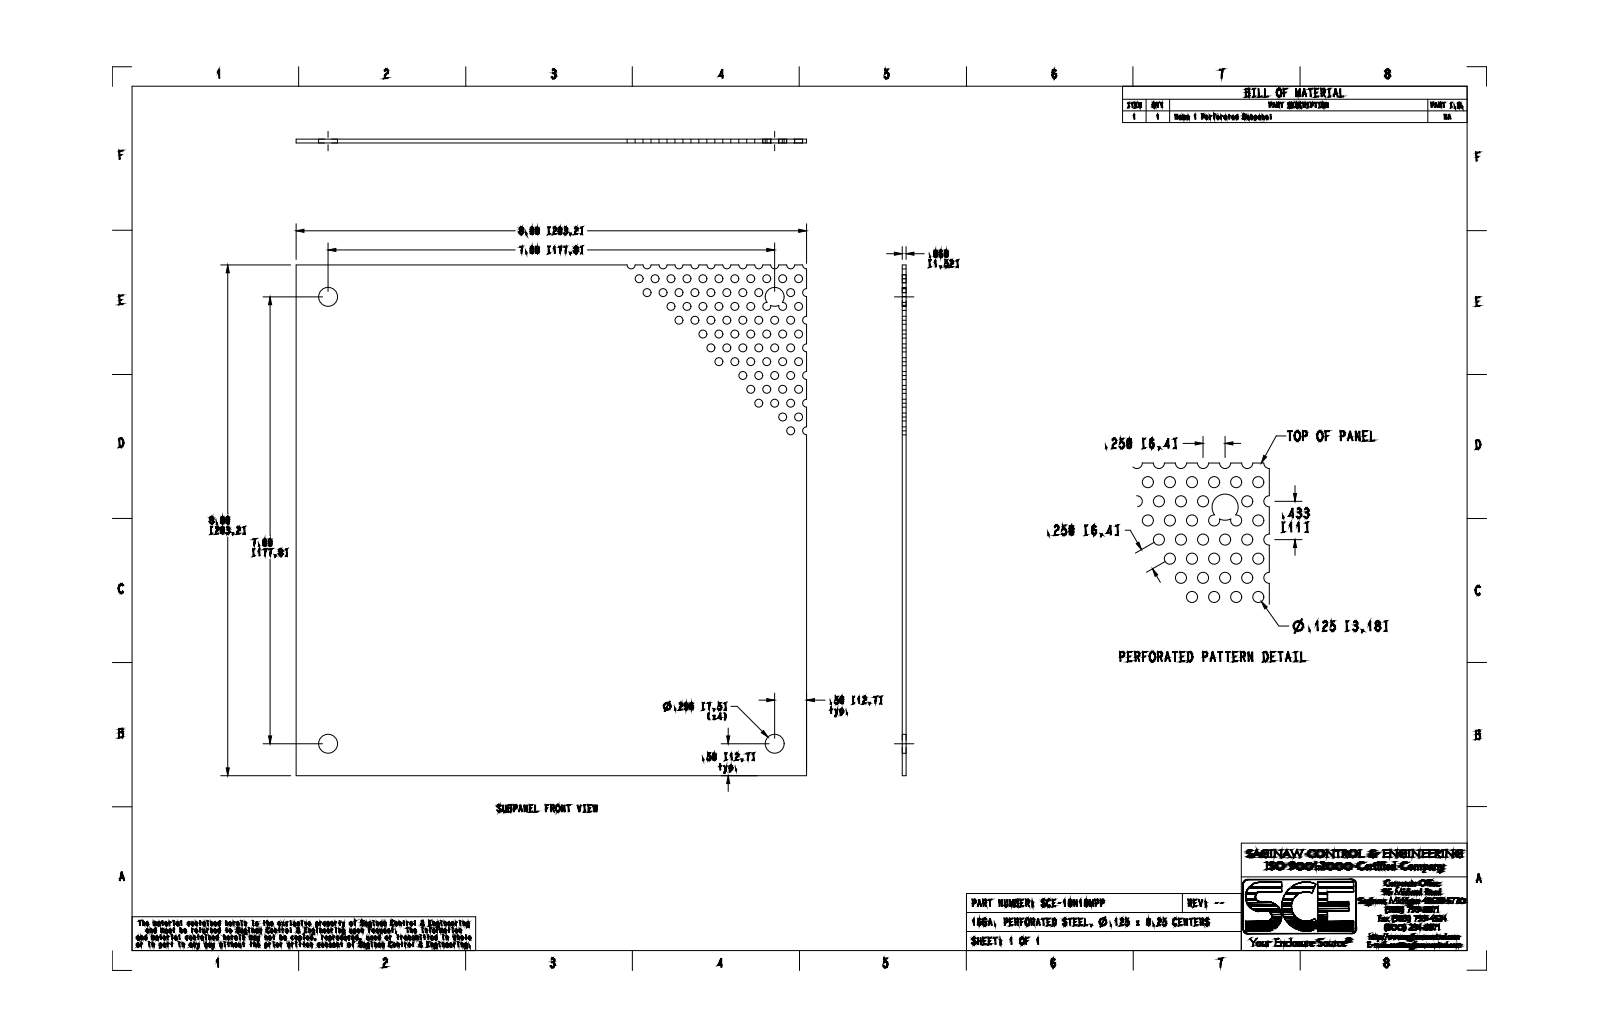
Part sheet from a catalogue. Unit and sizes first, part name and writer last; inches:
Units: inches
Overall size (bounding box): 8 × 8 × 0.06
Round holes (diameter × count): ⌀0.125 ×55, ⌀0.125 ×15, ⌀0.296 ×4
Partial cylindrical surfaces — rounded edges, fillets, slot ends (radius × count): R0.063 ×13, R0.062 ×5
Main face-to-face distances: 0.06, 8
Hole centre spacings: 0.25, 0.661, 0.5, 0.433, 0.433, 1.323, 1.09, 0.901
Volume: 3.766 in³ · Surface area: 129.4 in²
Bodies: 1 solid, 116 faces (23 planar, 93 cylindrical, 0 other)
Part name (STEP PRODUCT): SCE-10N10MPP
STEP written by: SolidWorks 2019 (CONFIG_CONTROL_DESIGN)
